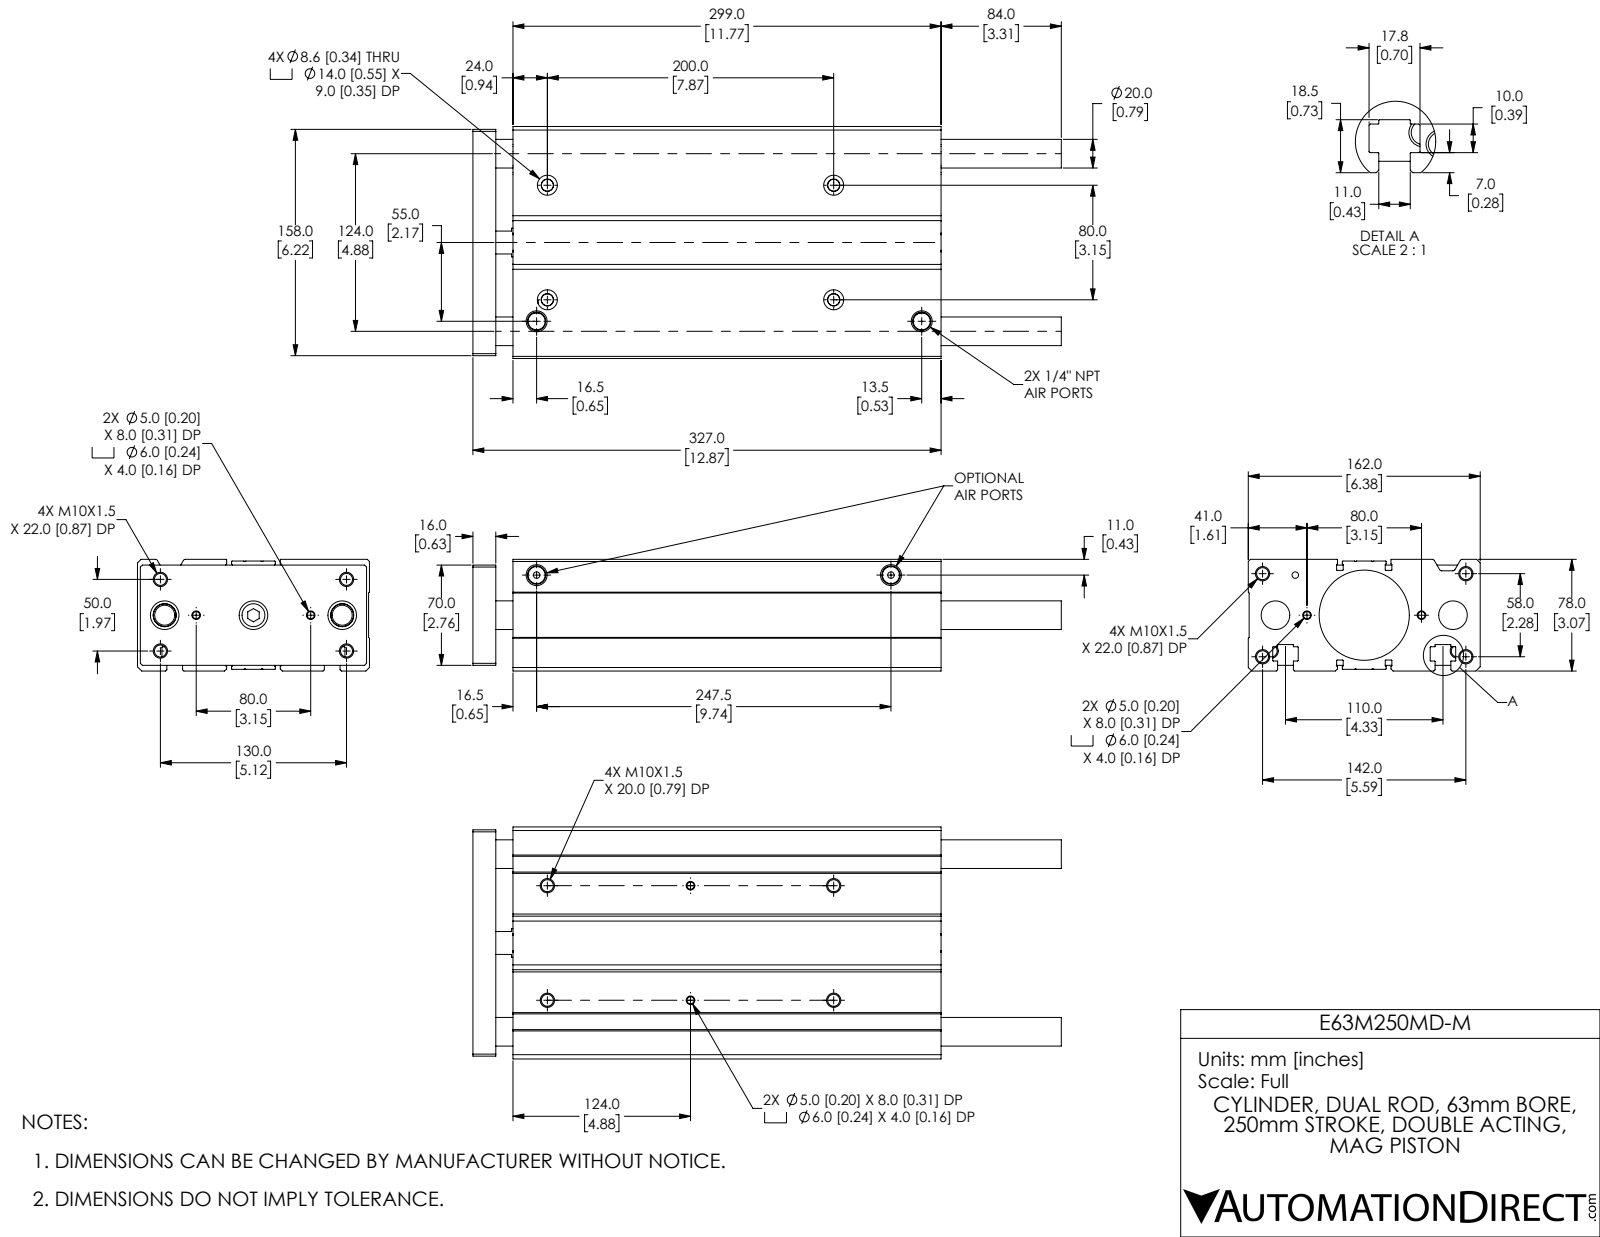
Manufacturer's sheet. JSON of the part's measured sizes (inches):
{"part_name": "E63M250MD-M_BODY; E63M250MD-M_ENDPLATE; E63M250MD-M", "step_written_by": "SolidWorks 2019 (CONFIG_CONTROL_DESIGN)", "units": "inches", "bodies": {"solids": 5, "faces": 421, "planar": 139, "cylindrical": 190, "other": 92}, "overall_size": [16.181, 6.378, 3.071], "volume_in3": 183.3, "surface_area_in2": 690.3, "round_holes": [[0.33, 12], [0.197, 4], [0.236, 4], [0.339, 4], [0.551, 4], [0.18, 3], [0.394, 3], [0.787, 3], [0.63, 2], [0.787, 1], [2.48, 1], [2.48, 1]], "round_bosses_or_shafts": [[0.63, 1]], "partial_cylinders_radius": [[0.008, 32], [0.016, 28], [0.059, 4], [0.012, 2]], "face_to_face_distances": [3.071, 0.047, 3.024, 0.024, 6.378, 0.157, 1.102, 0.63, 0.472, 4.331], "hole_center_spacings": [0.284, 0.991, 1.195, 1.392, 1.671, 2.139, 2.742, 3.019]}
